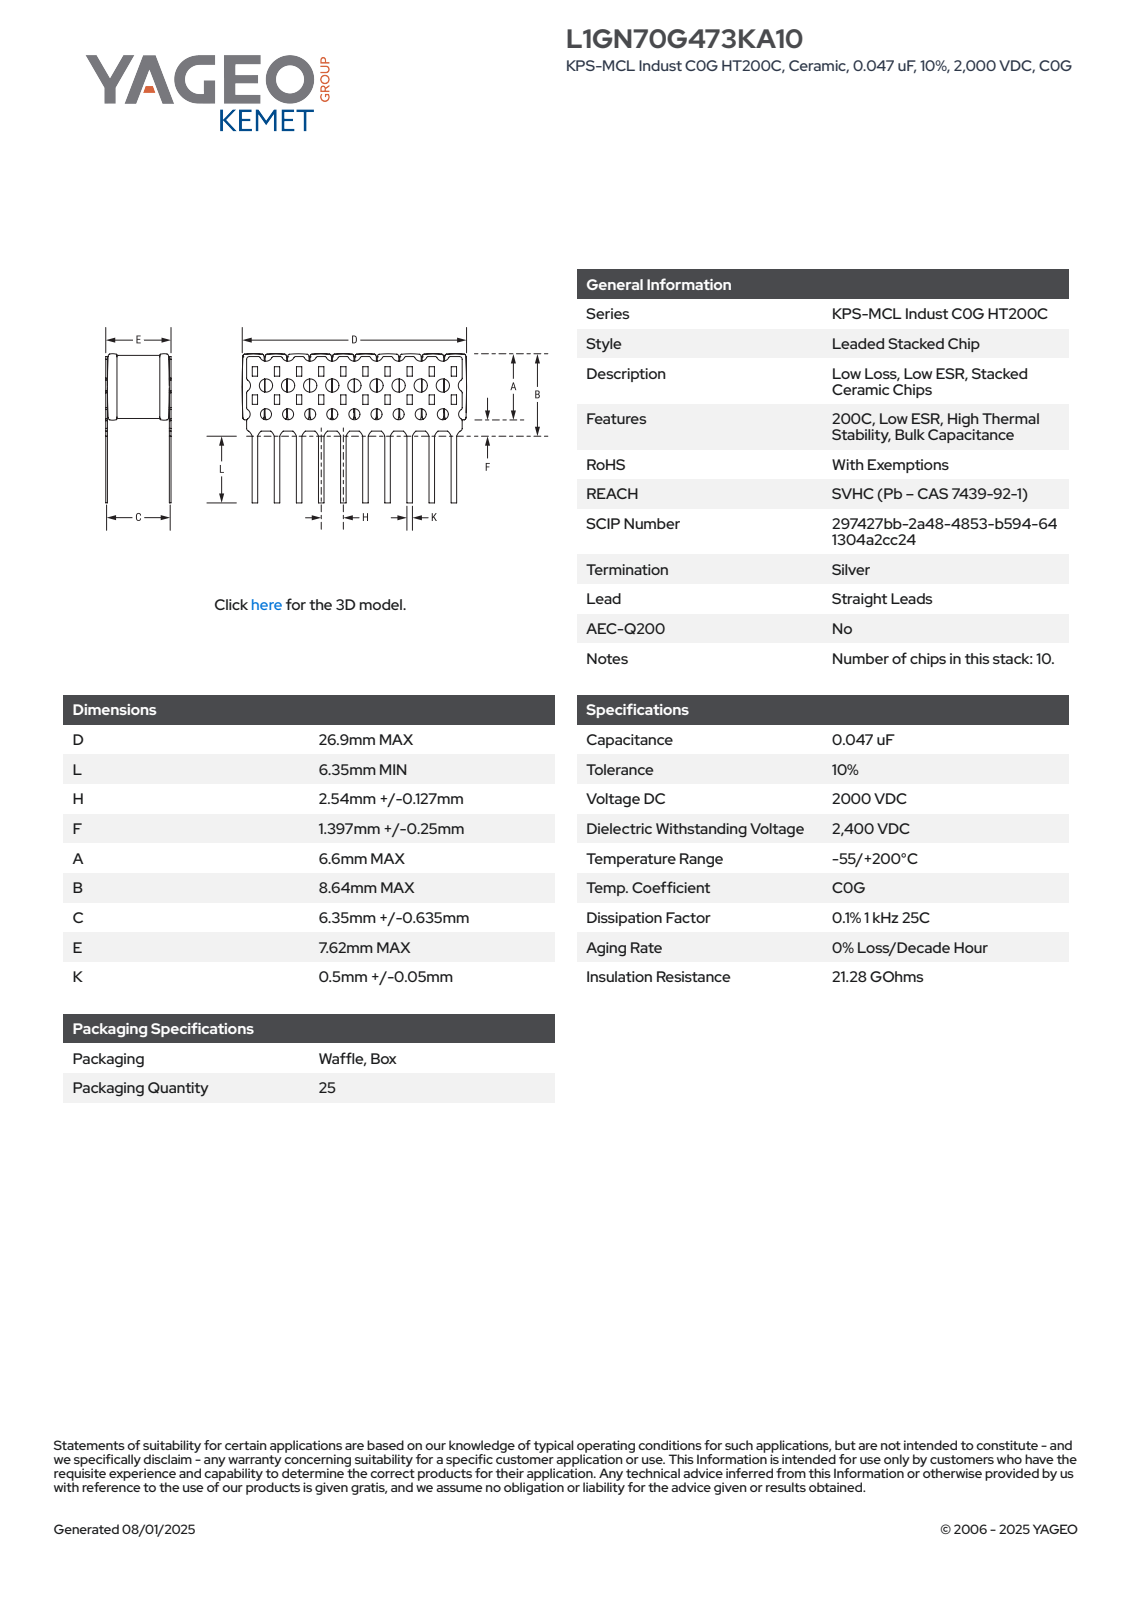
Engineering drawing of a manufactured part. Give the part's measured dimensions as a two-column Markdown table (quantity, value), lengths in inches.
| quantity | value |
| --- | --- |
| part name | CCSS_KLSS10_D26.9L6.35H2.667F1.647A6.6B8.64C6.985E7.62K0.55 |
| STEP written by | SolidWorks 2014 (AUTOMOTIVE_DESIGN) |
| units | inches |
| bodies | 7 solids, 298 faces (298 planar, 0 cylindrical, 0 other) |
| overall size | 1.06 × 0.563 × 0.275 |
| volume | 0.076 in³ |
| surface area | 2.598 in² |
| main face-to-face distances | 0.106, 0.318, 0.424, 0.53, 0.275, 0.098, 0.212, 0.212, 0.31, 0.416 |
